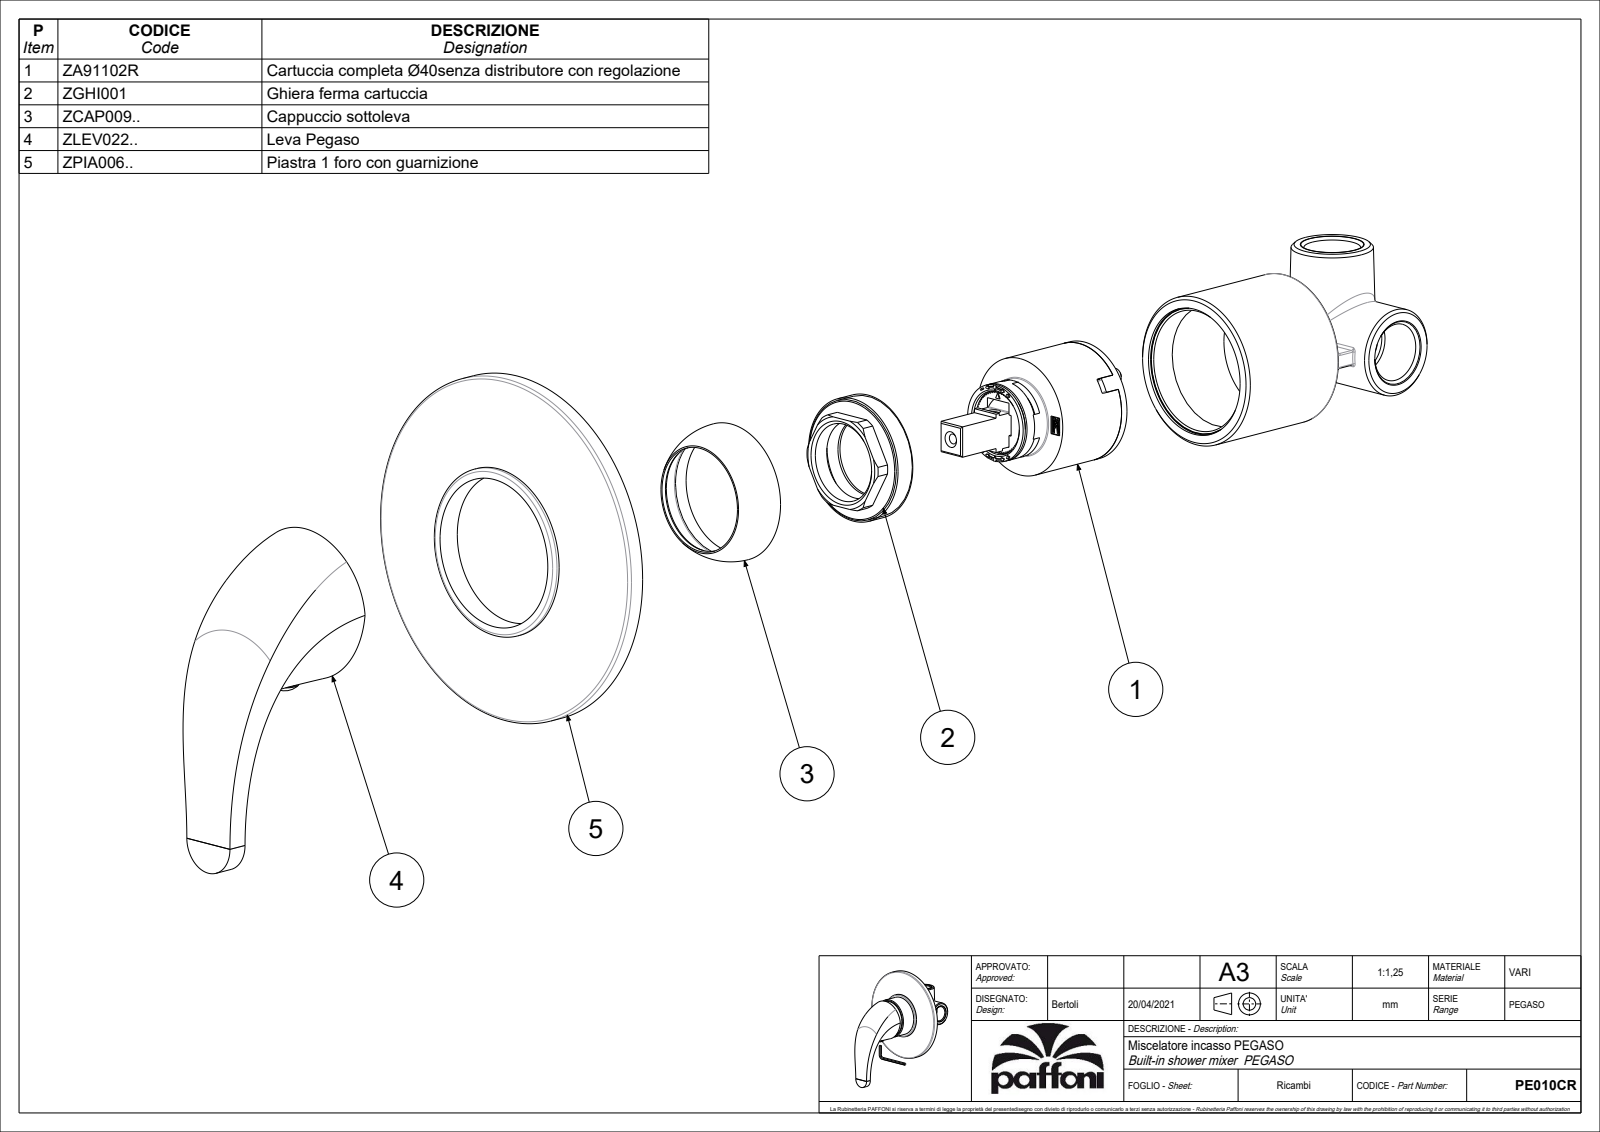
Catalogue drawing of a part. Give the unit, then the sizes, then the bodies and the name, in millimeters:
Units: millimetres
Overall size (bounding box): 141.6 × 131.57 × 116
Round holes (diameter × count): ⌀6 ×1
Round bosses / shafts (diameter × count): ⌀116 ×1, ⌀56.4 ×1, ⌀50 ×1, ⌀29 ×1, ⌀8 ×1, ⌀5 ×1
Partial cylindrical surfaces — rounded edges, fillets, slot ends (radius × count): R1 ×14, R0.5 ×4, R12 ×2, R3.5 ×1, R3.9 ×1
Main face-to-face distances: 45.51, 67.73, 22.22, 61, 23.95, 37.05, 34.5, 11.01, 56.72, 13.1
Volume: 261 822 mm³ · Surface area: 53 937 mm²
Bodies: 1 solid, 185 faces (42 planar, 51 cylindrical, 92 other)
Part name (STEP PRODUCT): PE010CR_SW0001
STEP written by: CREO PARAMETRIC BY PTC INC, 2022124 (CONFIG_CONTROL_DESIGN)
